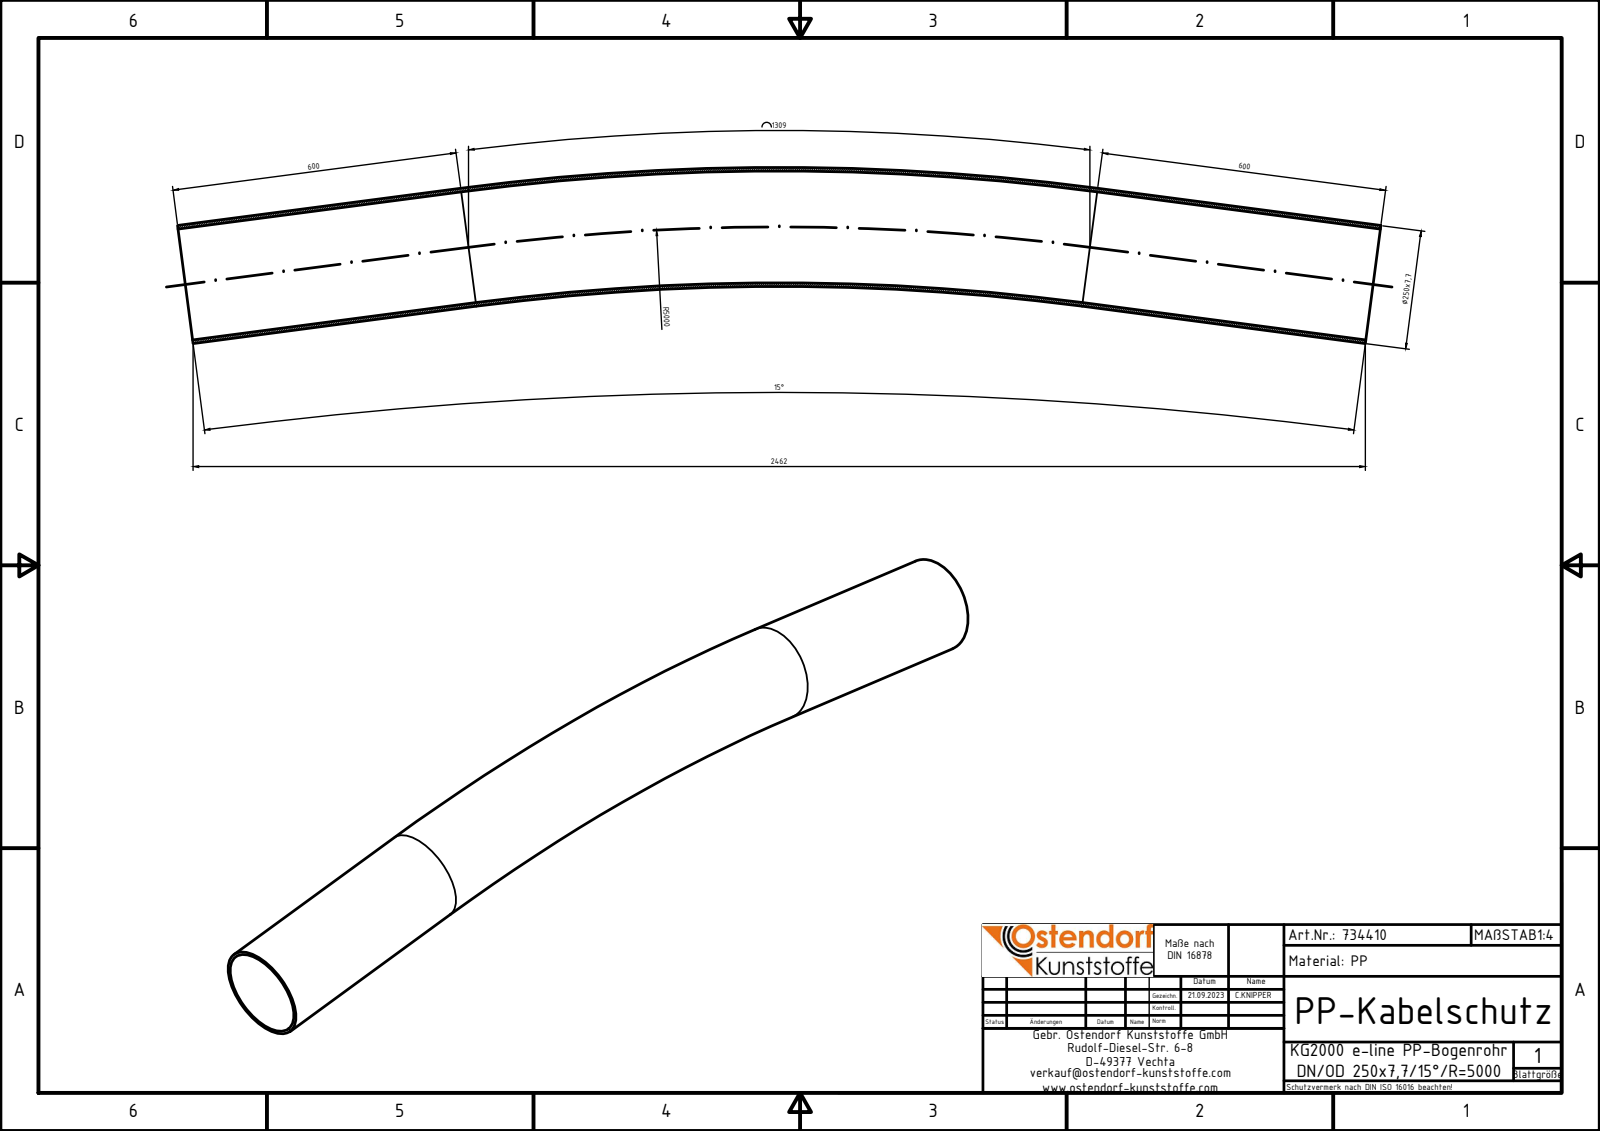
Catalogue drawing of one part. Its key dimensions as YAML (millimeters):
part_name: "734410z"
step_written_by: "Autodesk Inventor 2024 (AUTOMOTIVE_DESIGN)"
units: millimeters
bodies: {solids: 1, faces: 20, planar: 2, cylindrical: 6, other: 12}
overall_size: [2368.65, 358.93, 250]
volume: 13570000
surface_area: 3582000
round_holes:
  - {diameter: 234.6, count: 2}
  - {diameter: 239.6, count: 2}
round_bosses_or_shafts:
  - {diameter: 250, count: 2}
